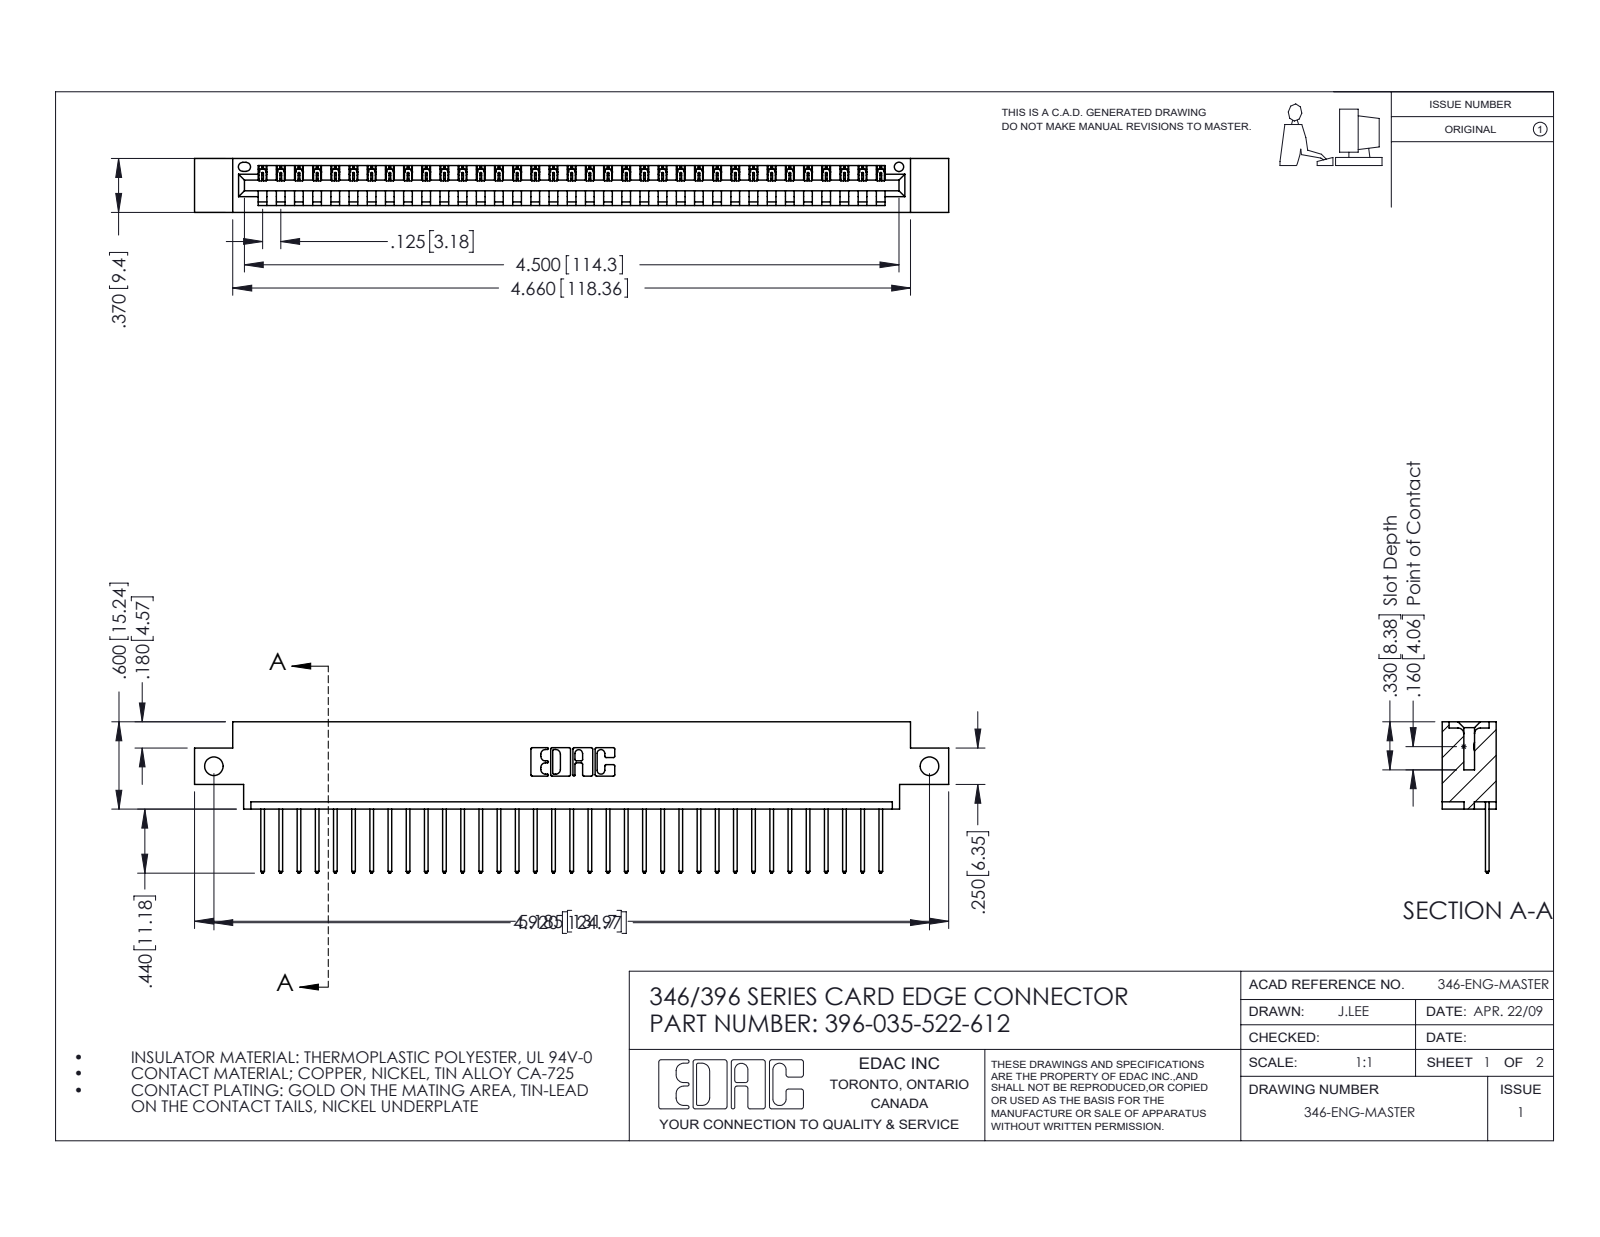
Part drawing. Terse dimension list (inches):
name: 396-035-522-612; 346 Part_0.170 Offset - Side Mount; 345-292-001_345-293-122
written by: SolidWorks 2016 (CONFIG_CONTROL_DESIGN)
unit: in
bodies: 36 solids, 2156 faces (1480 planar, 676 cylindrical, 0 other)
size: 5.185 × 1.04 × 0.37
volume: 0.752 in³; area: 23.97 in²
holes: 2× ⌀0.128, 1× ⌀0.064
rounds: 70× R0.006, 70× R0.01, 22× R0.01, 6× R0.007, 6× R0.031, 3× R0.026, 2× R0.031, 2× R0.04
face distances: 0.048, 0.322, 0.37, 0.25, 0.072, 0.298, 0.025, 0.148, 0.222, 0.1
hole spacings: 4.92
